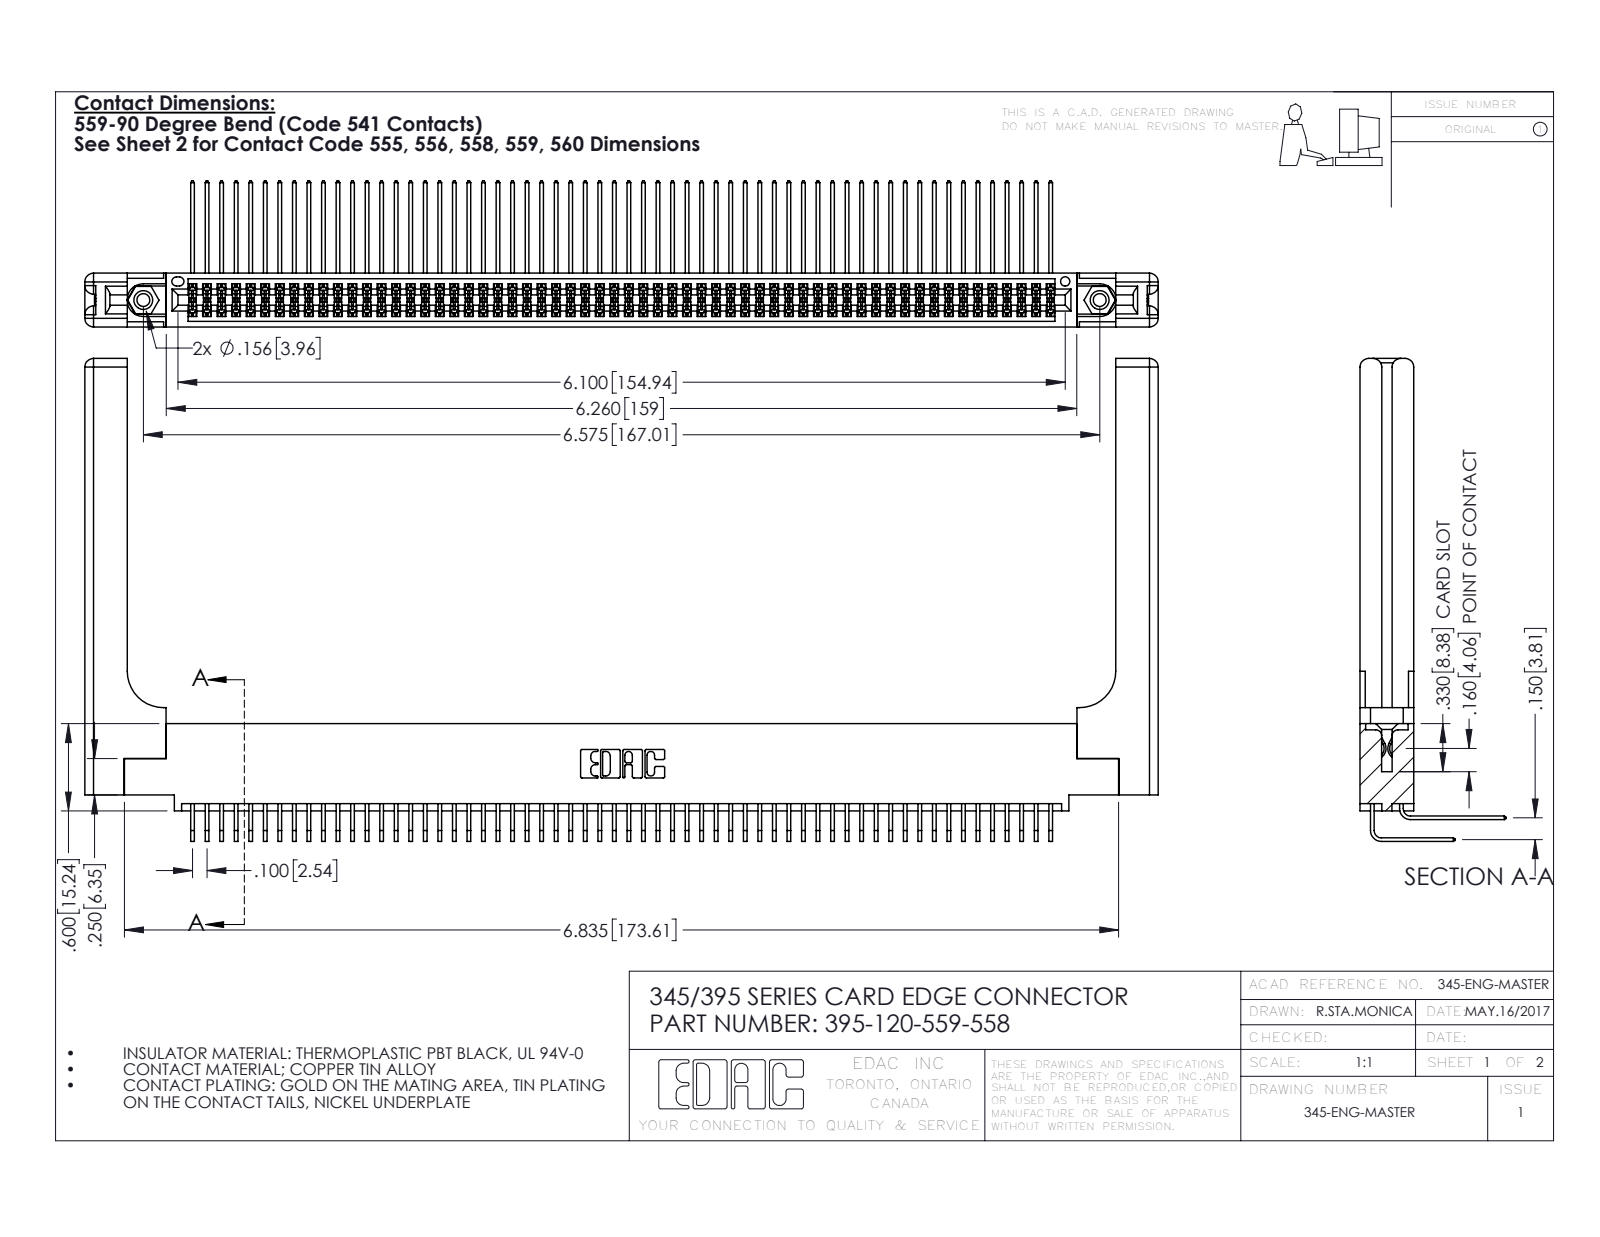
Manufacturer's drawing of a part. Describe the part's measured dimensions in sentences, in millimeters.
The part is named "345 Part_0.110 Offset - 0.156 Dia-TH; 345-220-058_345-220-058; 395-120-559-558; 345-292-001_559 Tail - 2 (+2 more)". Its 3-D file was written by "SolidWorks 2016 (CONFIG_CONTROL_DESIGN)". It is 125 solids with 6626 faces: 4432 planar, 2134 cylindrical and 60 other. Overall it measures 187.4 by 84.3 by 25.5 millimeters. Its volume is 27 460 cubic millimeters and its surface area 36 830 square millimeters. Round holes: 2 of diameter 2.3, 2 of diameter 3.2, 2 of diameter 4, 1 of diameter 1.6. Round bosses or shafts: 2 of diameter 3.9. Partial cylindrical surfaces (rounded edges, fillets, slot ends): 180 of radius 0.2, 22 of radius 0.3, 16 of radius 1.5, 6 of radius 0.2, 6 of radius 0.8, 3 of radius 0.7, 2 of radius 0.4, 2 of radius 0.5. The main face-to-face distances are 1.8, 7.6, 9.4, 2.5, 6.9, 0.6, 5.1, 5.7, 4.4, 3.8. The hole center spacings are 6.9, 161, 167.
